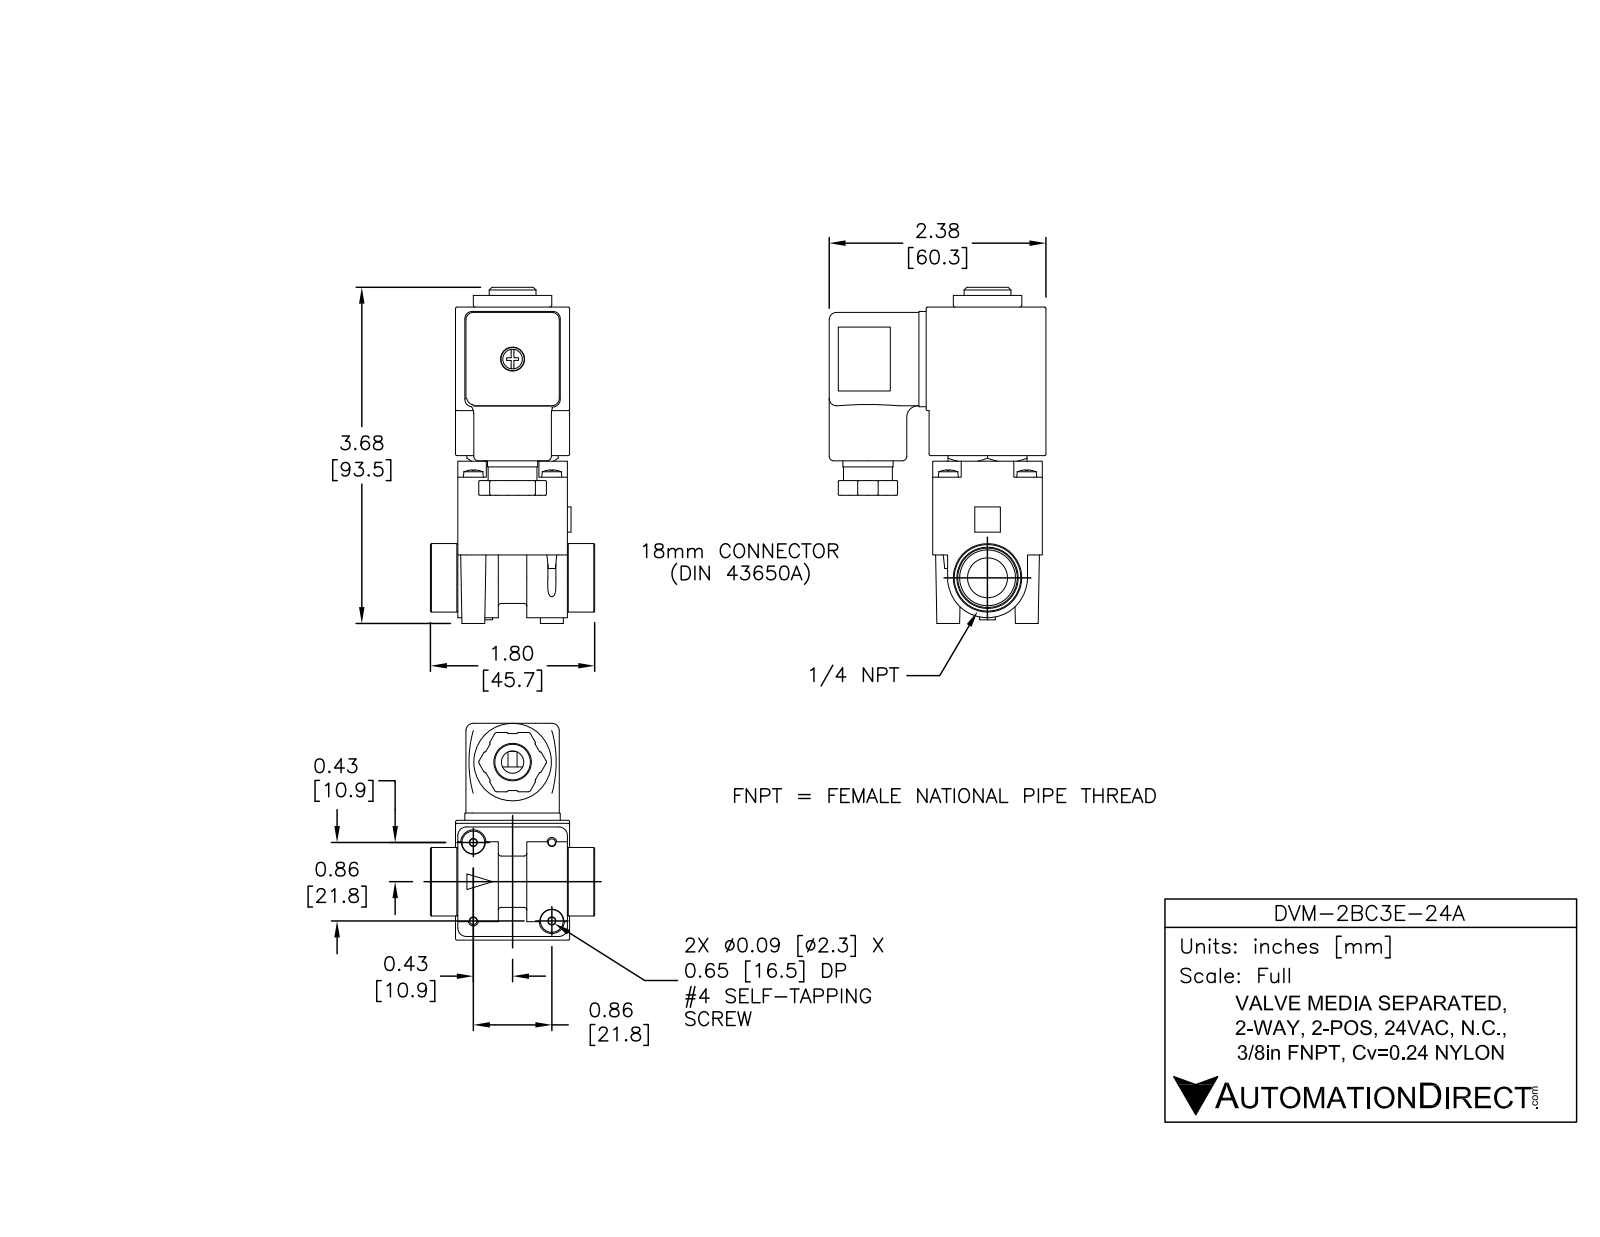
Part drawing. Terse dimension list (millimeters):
name: DVM-2BC3E-24A
written by: SolidWorks 2015 (AUTOMOTIVE_DESIGN)
unit: mm
bodies: 14 solids, 1775 faces (895 planar, 351 cylindrical, 529 other)
size: 93.5 × 60.3 × 45.7
volume: 83 820 mm³; area: 43 890 mm²
holes: 4× ⌀2.8, 2× ⌀1.5, 2× ⌀2.3, 2× ⌀8, 1× ⌀3, 1× ⌀4, 1× ⌀5.2, 1× ⌀6.2, 1× ⌀6.4, 1× ⌀6.7, 1× ⌀9.9, 1× ⌀10.2
bosses: 4× ⌀5.5, 4× ⌀3.2, 1× ⌀22.2, 1× ⌀22.2, 1× ⌀21.6, 1× ⌀20.5, 1× ⌀17.3, 1× ⌀13.6
rounds: 54× R0.3, 21× R0.1, 17× R0.4, 12× R0.5, 12× R0.8, 12× R0.8, 12× R2, 8× R1.3
face distances: 31.8, 30.5, 4.1, 27.6, 1.2, 3.5, 24.7, 31.1, 24.5, 1
hole spacings: 15.4, 15.4, 17.4, 21.8, 21.8, 24.9, 30.9, 37
